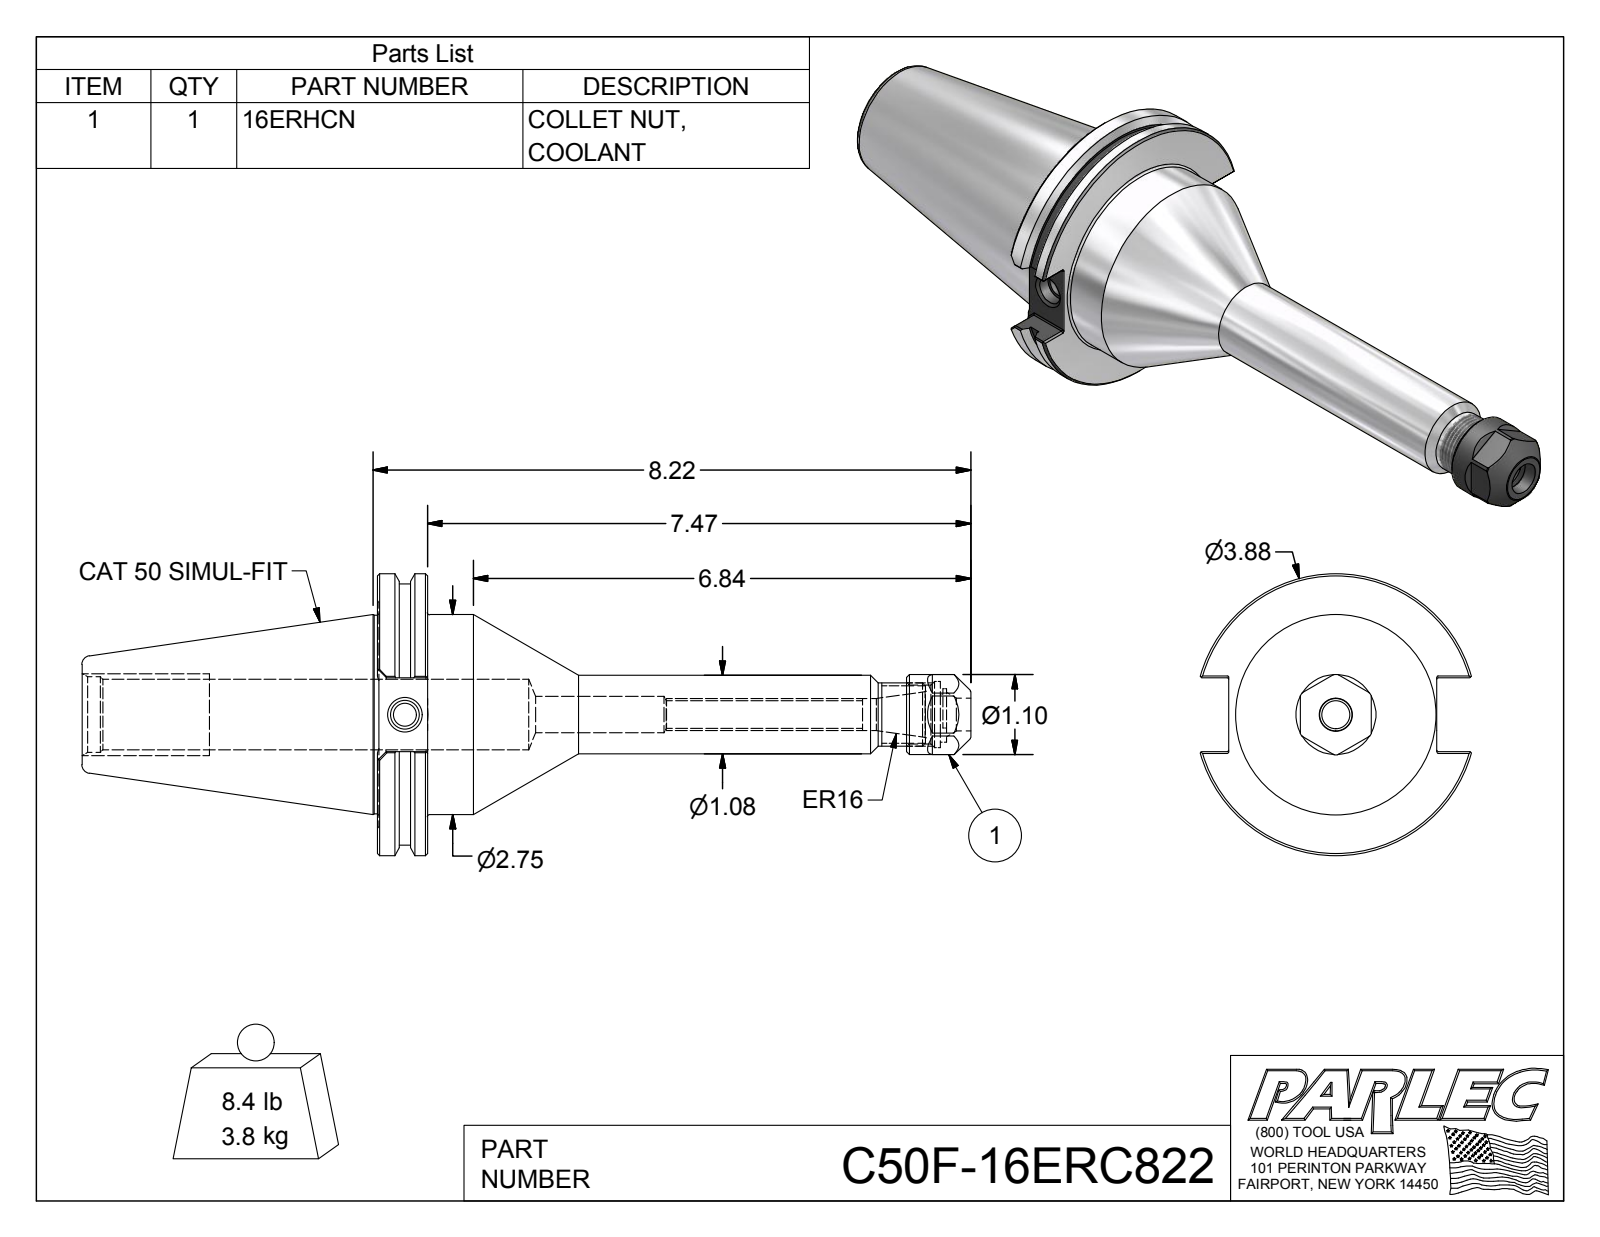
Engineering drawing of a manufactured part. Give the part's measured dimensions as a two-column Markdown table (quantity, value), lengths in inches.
| quantity | value |
| --- | --- |
| part name | C50F-16ERC822; C50F-16ER8-1; 16ERHCN |
| STEP written by | Autodesk Inventor 2012 (AUTOMOTIVE_DESIGN) |
| units | inches |
| bodies | 2 solids, 128 faces (51 planar, 35 cylindrical, 42 other) |
| overall size | 12.22 × 3.875 × 3.729 |
| volume | 29.74 in³ |
| surface area | 114.6 in² |
| round holes (diameter × count) | 0.315 × 1, 0.383 × 1, 0.399 × 1, 0.44 × 1, 0.453 × 1, 0.5 × 1, 0.661 × 1, 0.807 × 1, 0.906 × 1, 0.97 × 1, 1.038 × 1 |
| round bosses / shafts (diameter × count) | 3.875 × 1, 3.594 × 1, 2.75 × 1, 2.73 × 1, 1.102 × 1, 1.08 × 1, 0.866 × 1 |
| partial cylindrical surfaces (radius × count) | 0.02 × 12, 0.354 × 1 |
| main face-to-face distances | 0.691, 0.02, 0.671, 0.979, 4.059, 4.079, 4.75, 2.86, 1.015, 11.799 |
| hole center spacings | 0.051 |
